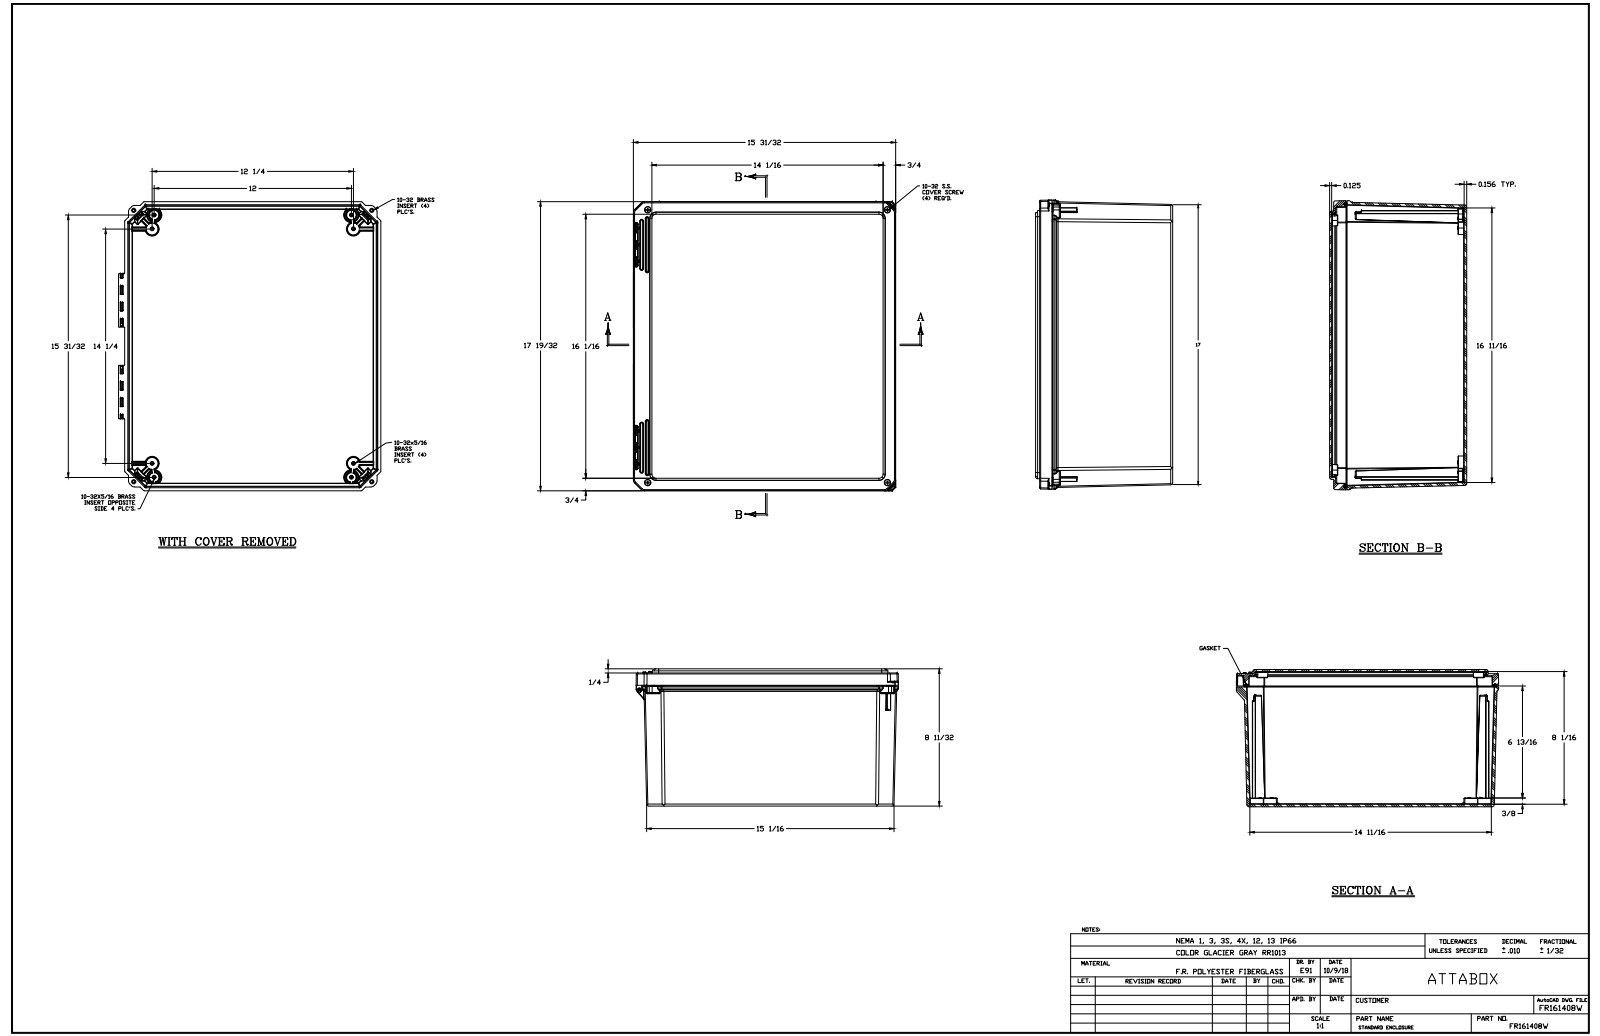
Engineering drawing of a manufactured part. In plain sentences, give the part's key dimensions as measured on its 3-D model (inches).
The part is named "FR161408W". Its 3-D file was written by "SolidWorks 2018 (AUTOMOTIVE_DESIGN)". It is 27 solids with 2150 faces: 729 planar, 786 cylindrical and 635 other. Overall it measures 17.602 by 15.962 by 8.341 inches. Its volume is 182.9 cubic inches and its surface area 2 218 square inches. Round holes: 16 of diameter 0.156, 8 of diameter 0.152, 4 of diameter 0.252, 4 of diameter 0.253, 2 of diameter 0.219, 2 of diameter 0.227, 2 of diameter 0.313, 1 of diameter 0.137. Round bosses or shafts: 16 of diameter 0.246, 4 of diameter 0.45, 4 of diameter 0.199, 1 of diameter 0.435, 1 of diameter 0.435. Partial cylindrical surfaces (rounded edges, fillets, slot ends): 175 of radius 0.01, 80 of radius 0.005, 57 of radius 0.02, 45 of radius 0.03, 24 of radius 0.03, 24 of radius 0.09, 24 of radius 0.096, 22 of radius 0.125. The main face-to-face distances are 0.125, 0.156, 8.185, 8.341, 8.217, 8.061, 0.18, 0.181, 0.25, 0.375. The hole center spacings are 13.296, 13.469, 0.865, 1.33, 1.652, 12.155, 15.106, 15.461.
